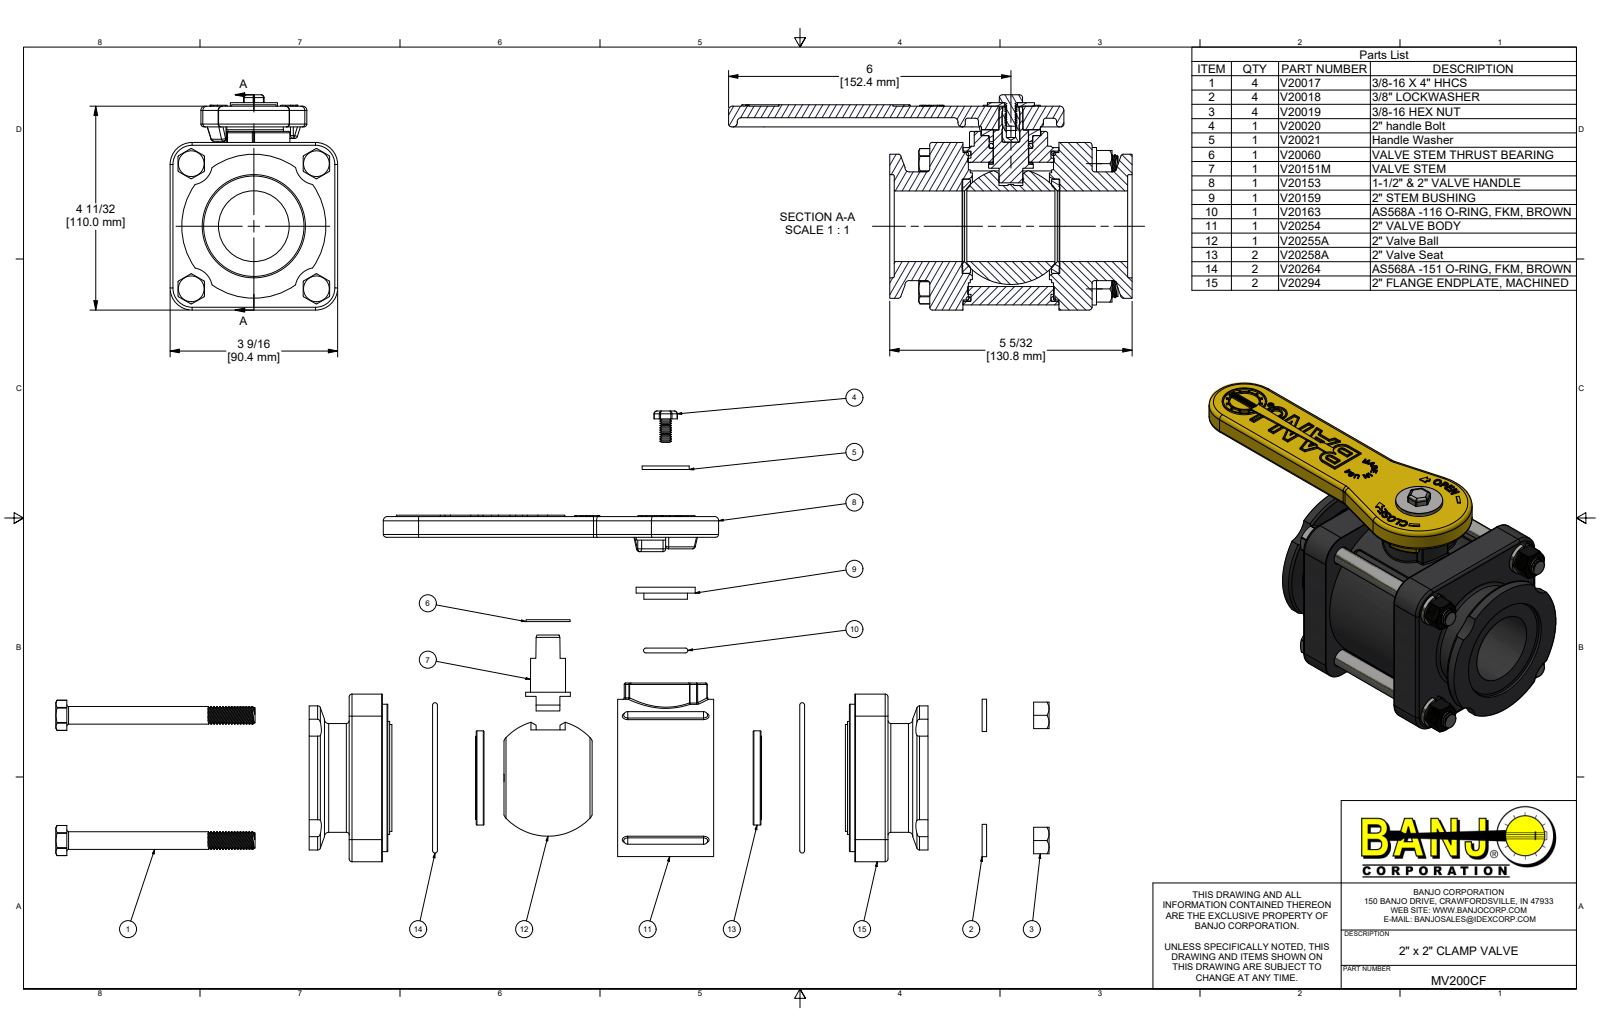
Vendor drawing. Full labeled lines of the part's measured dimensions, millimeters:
Part name (STEP PRODUCT): MV200CF; V20254; V20255A; V20255AM (+8 more)
STEP written by: Autodesk Inventor 2022 (AUTOMOTIVE_DESIGN)
Units: millimetres
Bodies: 28 solids, 1734 faces (638 planar, 510 cylindrical, 586 other)
Overall size (bounding box): 217.8 × 116.1 × 90.4
Volume: 640 700 mm³ · Surface area: 183 700 mm²
Round holes (diameter × count): ⌀4.2 ×10, ⌀7.8 ×4, ⌀9.8 ×4, ⌀10.3 ×4, ⌀2.3 ×1, ⌀5 ×1, ⌀7.1 ×1, ⌀8.9 ×1, ⌀9.5 ×1, ⌀16.1 ×1, ⌀19.1 ×1, ⌀19.1 ×1
Round bosses / shafts (diameter × count): ⌀8.2 ×60, ⌀17.4 ×4, ⌀9.5 ×4, ⌀84.8 ×1, ⌀79.5 ×1, ⌀73.4 ×1, ⌀61 ×1, ⌀58.7 ×1
Partial cylindrical surfaces — rounded edges, fillets, slot ends (radius × count): R1.5 ×40, R0.8 ×26, R2.3 ×12, R3.2 ×9, R4.1 ×8, R0.4 ×4, R2.4 ×4, R8.1 ×4
Main face-to-face distances: 17.9, 69.7, 87.6, 90.4, 20.8, 66.8, 2.9, 48.9, 6.2, 51.8
Hole centre spacings: 34.6, 59, 66.9, 17.9, 24.8, 42.7, 59.9, 71.6
